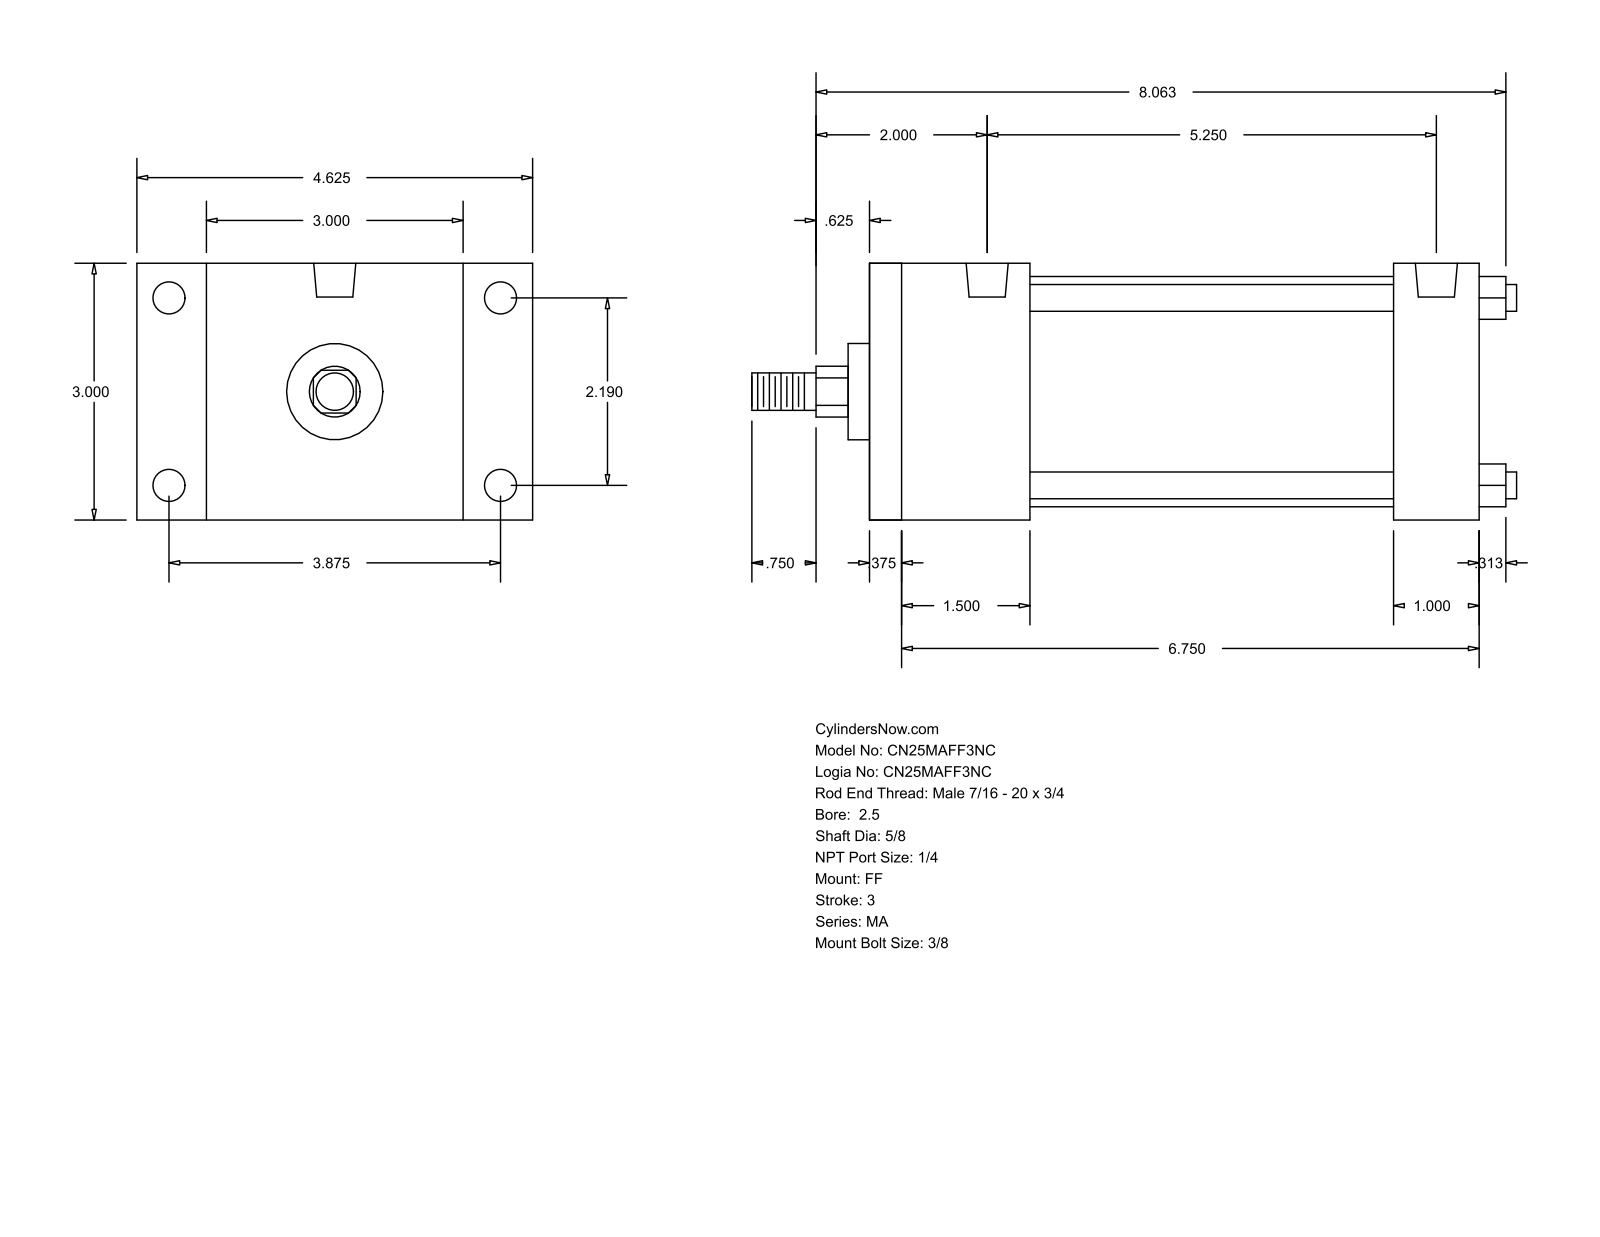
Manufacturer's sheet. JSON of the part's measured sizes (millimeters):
{"part_name": "MA_FF__0250_0.625", "step_written_by": "GSSL Pune (CONFIG_CONTROL_DESIGN)", "units": "millimeters", "bodies": {"solids": 0, "faces": 92, "planar": 64, "cylindrical": 28, "other": 0}, "overall_size": [227.01, 117.47, 76.2], "round_holes": [[7.94, 4], [9.53, 4], [12.49, 2]], "round_bosses_or_shafts": [[7.94, 4], [68.33, 1], [28.57, 1], [15.88, 1], [11.11, 1]], "partial_cylinders_radius": [[7.54, 1]], "face_to_face_distances": [76.2, 180.97, 171.45, 9.52, 25.4, 47.62, 155.57, 38.1, 146.05, 107.95], "hole_center_spacings": [55.62, 98.42, 113.05, 133.35]}
